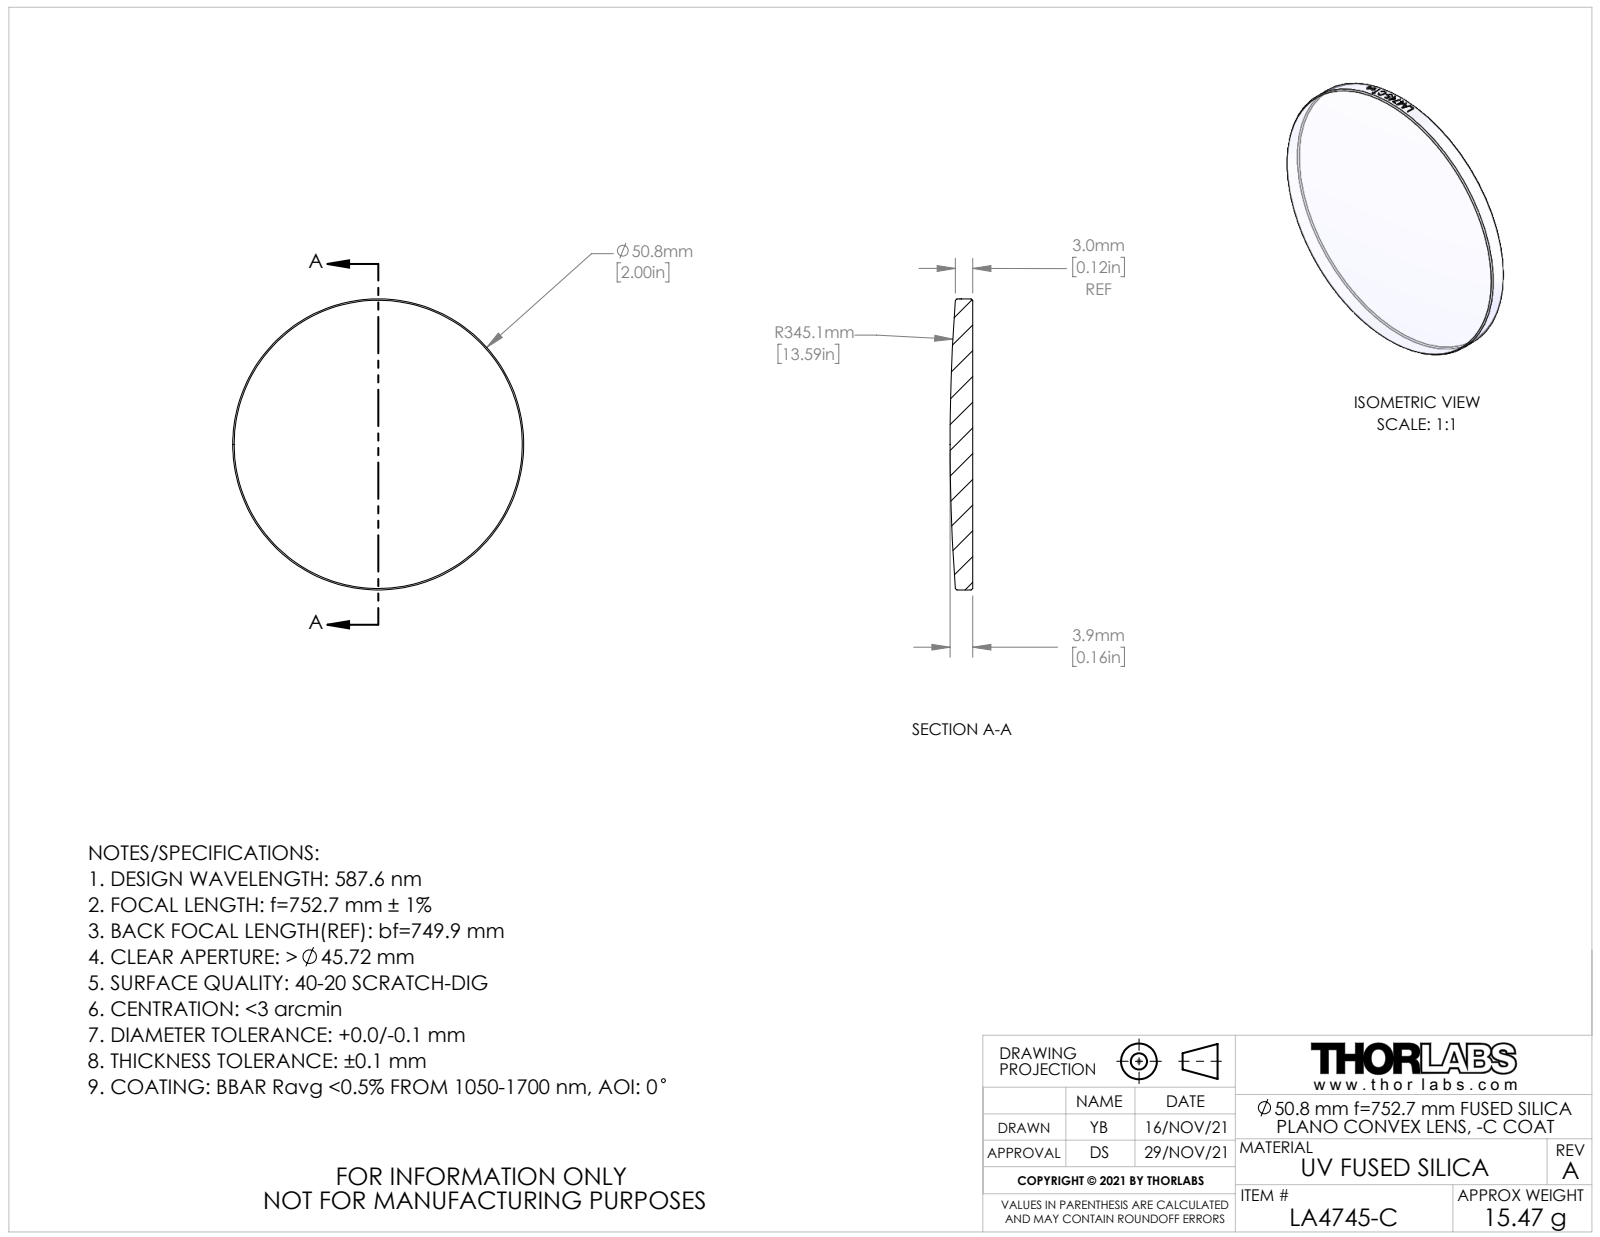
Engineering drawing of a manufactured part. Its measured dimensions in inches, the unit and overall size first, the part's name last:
Units: inches
Overall size (bounding box): 2 × 2 × 0.155
Round bosses / shafts (diameter × count): ⌀2 ×1
Volume: 0.429 in³ · Surface area: 6.96 in²
Bodies: 1 solid, 24 faces (1 planar, 17 cylindrical, 6 other)
Part name (STEP PRODUCT): CTN018149; CTN018083-E0W
STEP written by: SolidWorks 2018 (AUTOMOTIVE_DESIGN)
